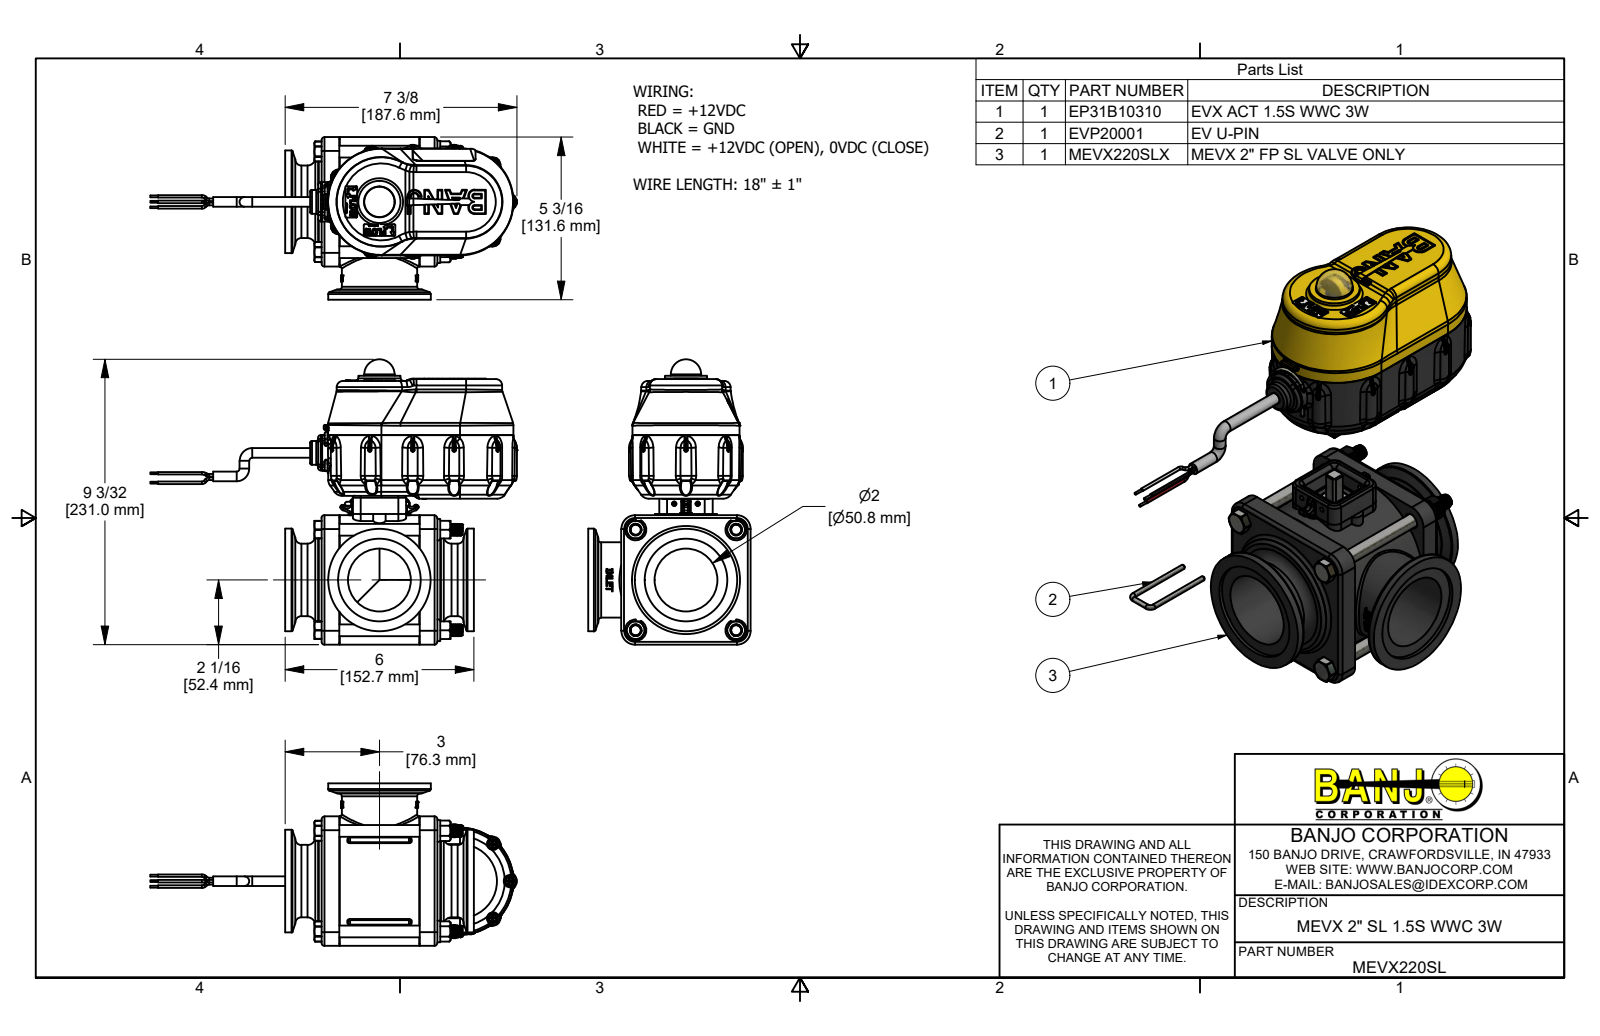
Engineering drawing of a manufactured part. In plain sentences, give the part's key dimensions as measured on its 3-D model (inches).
The part is named "MEVX220SL; MEVX220SLX; MEVX25354AS; MEVX25354ASX (+8 more)". Its 3-D file was written by "Autodesk Inventor 2022 (CONFIG_CONTROL_DESIGN)". It is 97 solids with 11929 faces: 3279 planar, 3417 cylindrical and 5233 other. Overall it measures 11.685 by 9.095 by 5.181 inches. Its volume is 76.72 cubic inches and its surface area 760.4 square inches. Round holes: 11 of diameter 0.095, 11 of diameter 0.15, 7 of diameter 0.08, 4 of diameter 0.107, 4 of diameter 0.126, 4 of diameter 0.136, 4 of diameter 0.148, 4 of diameter 0.15, 4 of diameter 0.17, 4 of diameter 0.307, 4 of diameter 0.385, 4 of diameter 0.46. Round bosses or shafts: 60 of diameter 0.324, 17 of diameter 0.25, 15 of diameter 0.08, 11 of diameter 0.14, 11 of diameter 0.108, 11 of diameter 0.085, 6 of diameter 0.058, 5 of diameter 0.375. Partial cylindrical surfaces (rounded edges, fillets, slot ends): 180 of radius 0.013, 145 of radius 0.04, 99 of radius 0.01, 96 of radius 0.02, 57 of radius 0.005, 47 of radius 0.03, 33 of radius 0.015, 28 of radius 0.08. The main face-to-face distances are 0.1, 2.565, 0.06, 0.645, 3.045, 0.729, 2.485, 0.56, 3.13, 0.085. The hole center spacings are 2.265, 2.715, 3.204, 1.662, 1.774, 2.458, 2.69, 2.73.
